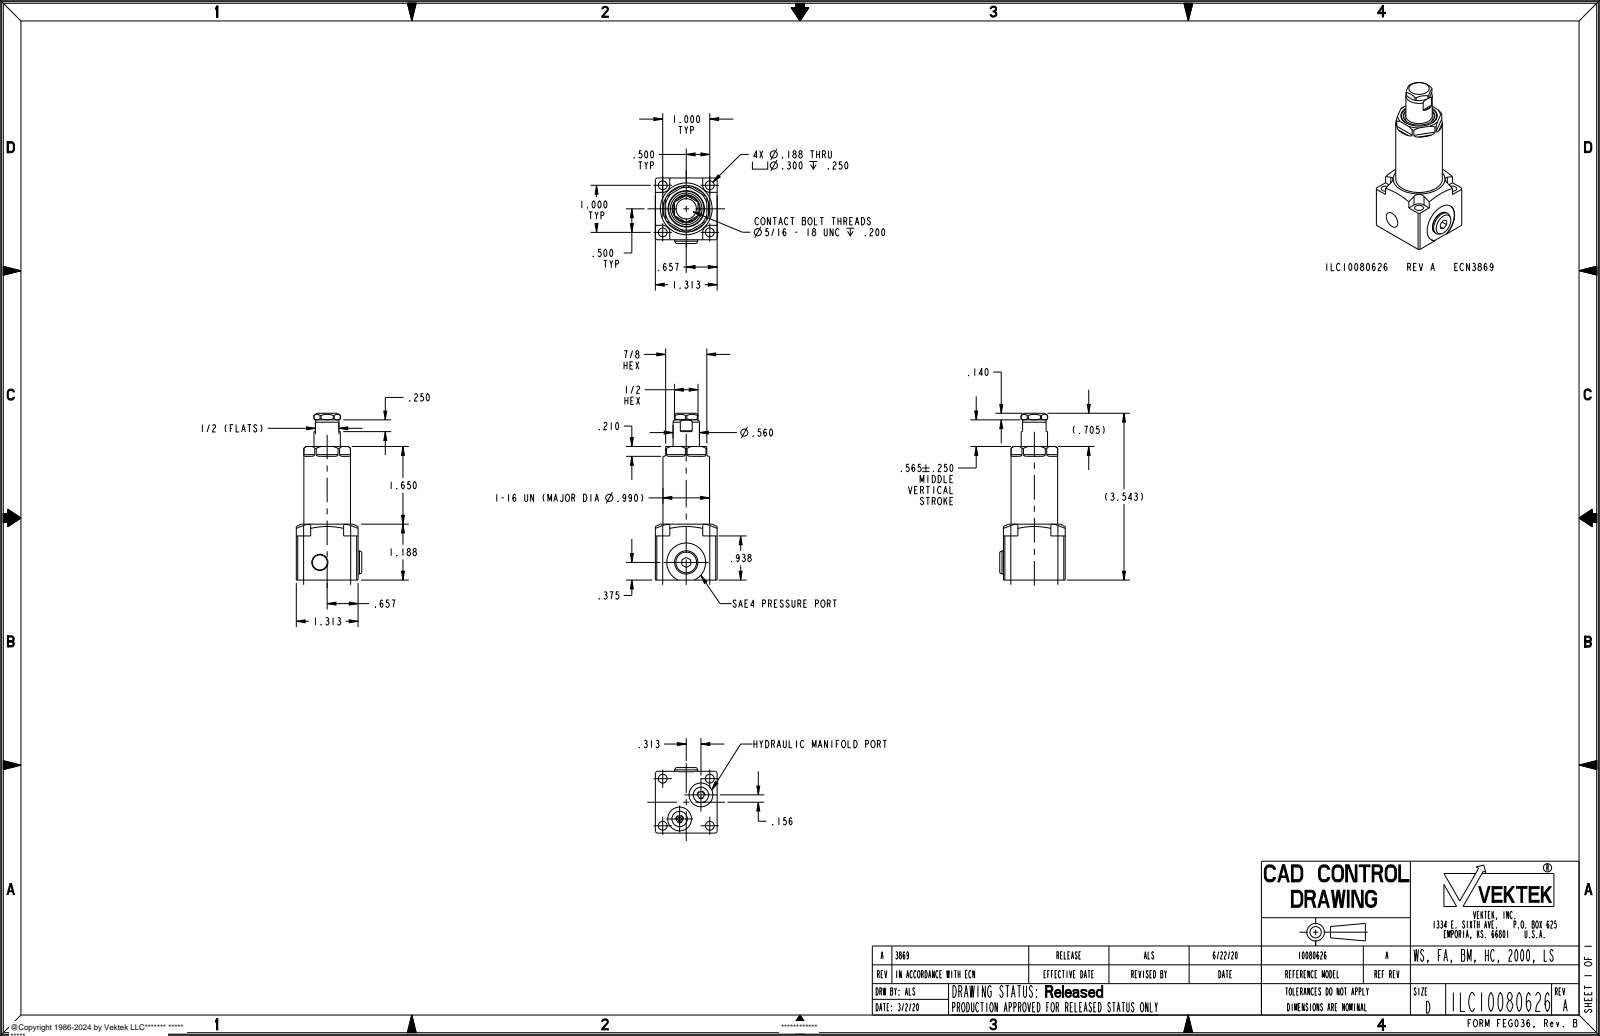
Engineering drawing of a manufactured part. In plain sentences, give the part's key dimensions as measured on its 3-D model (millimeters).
The part is named "ILC10080626". Its 3-D file was written by "PRO/ENGINEER BY PARAMETRIC TECHNOLOGY CORPORATION, 2013320 (CONFIG_CONTROL_DESIGN)". It is 1 solid with 177 faces: 70 planar, 63 cylindrical and 44 other. Overall it measures 90 by 35.3 by 33.4 millimeters. Its volume is 50 780 cubic millimeters and its surface area 13 840 square millimeters. Round holes: 4 of diameter 4.8, 2 of diameter 3.5, 2 of diameter 4.2, 2 of diameter 8.3, 2 of diameter 12.8, 1 of diameter 2, 1 of diameter 6.9, 1 of diameter 10, 1 of diameter 17, 1 of diameter 21. Round bosses or shafts: 1 of diameter 25.1, 1 of diameter 19.1, 1 of diameter 14.2, 1 of diameter 11.1, 1 of diameter 11.1, 1 of diameter 8. Partial cylindrical surfaces (rounded edges, fillets, slot ends): 6 of radius 0.9, 4 of radius 3.8, 2 of radius 0.5, 1 of radius 7.1. The main face-to-face distances are 33.4, 33.1, 23.8, 4.7, 2, 21.8, 22.2, 6.4, 30.1, 28.2. The hole center spacings are 18, 25.4, 35.9, 8.9, 9.7, 9.8, 10, 16.7.
